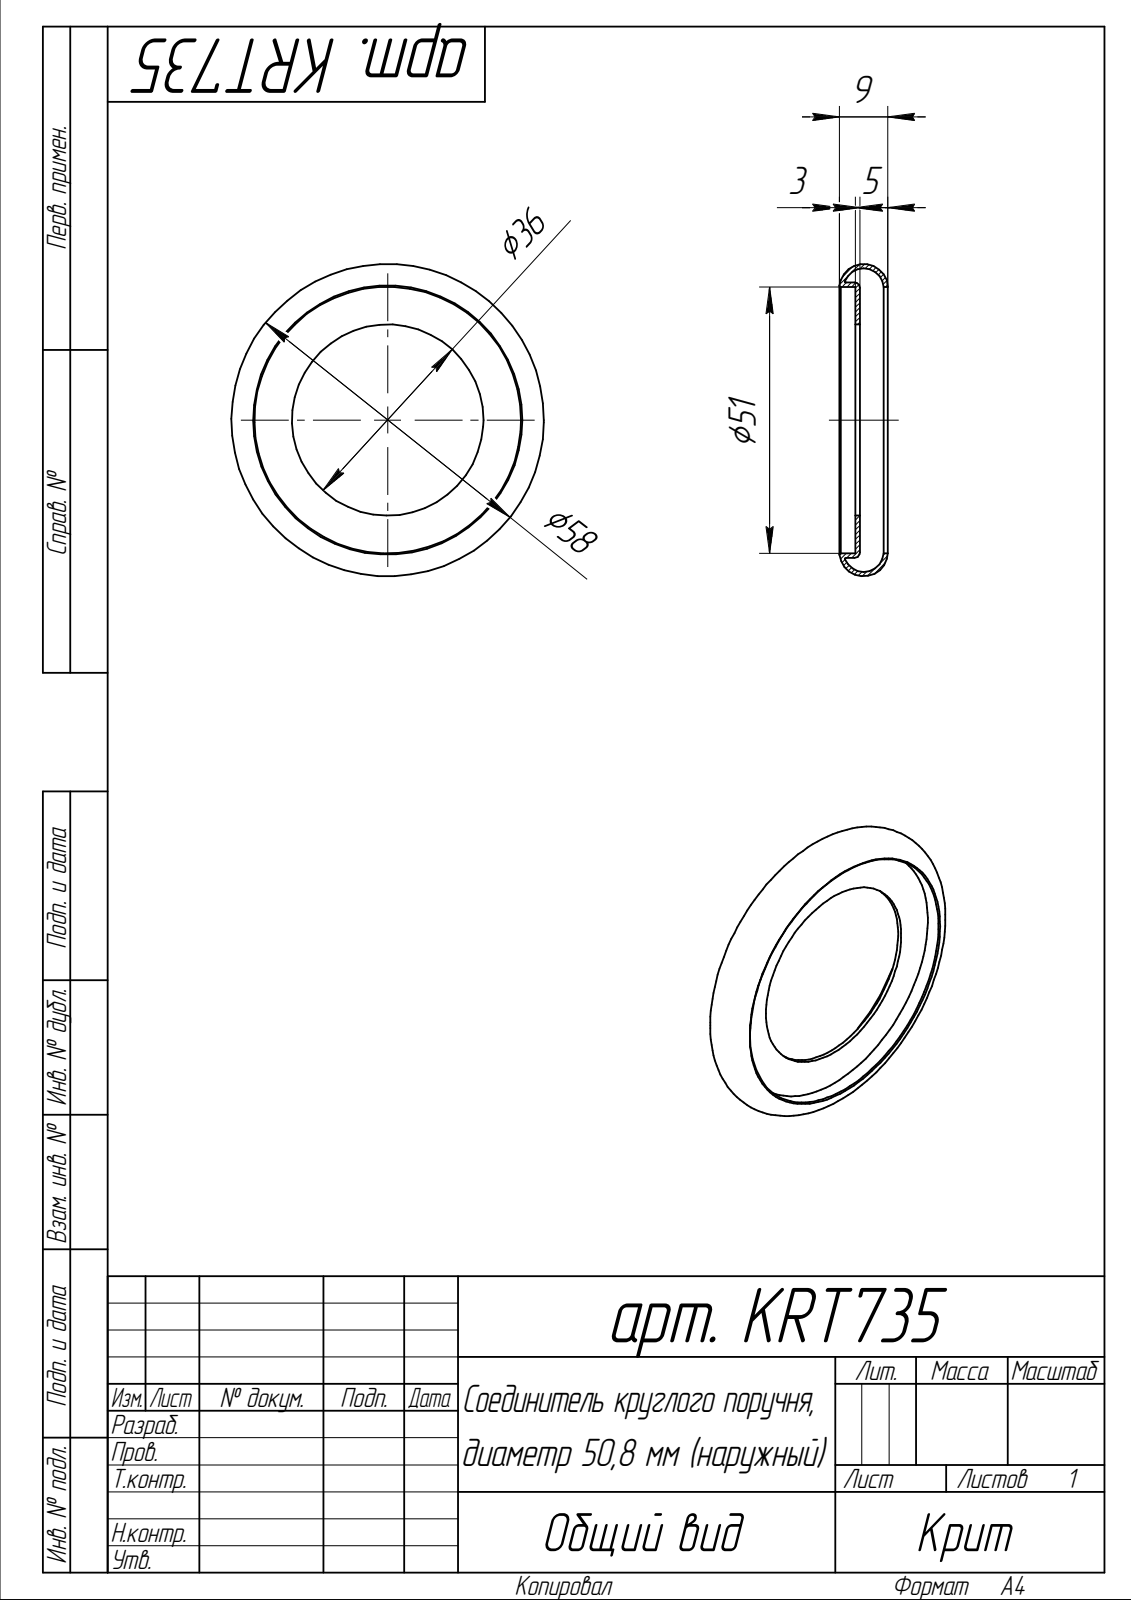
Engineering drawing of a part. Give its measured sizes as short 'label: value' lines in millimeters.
name: арт. KRT735
written by: SolidWorks 2014 (AUTOMOTIVE_DESIGN)
unit: mm
bodies: 1 solid, 20 faces (2 planar, 6 cylindrical, 12 other)
size: 58 × 58 × 8.98
volume: 2 784 mm³; area: 7 138 mm²
holes: 1× ⌀35.5, 1× ⌀49.5
bosses: 1× ⌀51.1
face distances: 0.8
